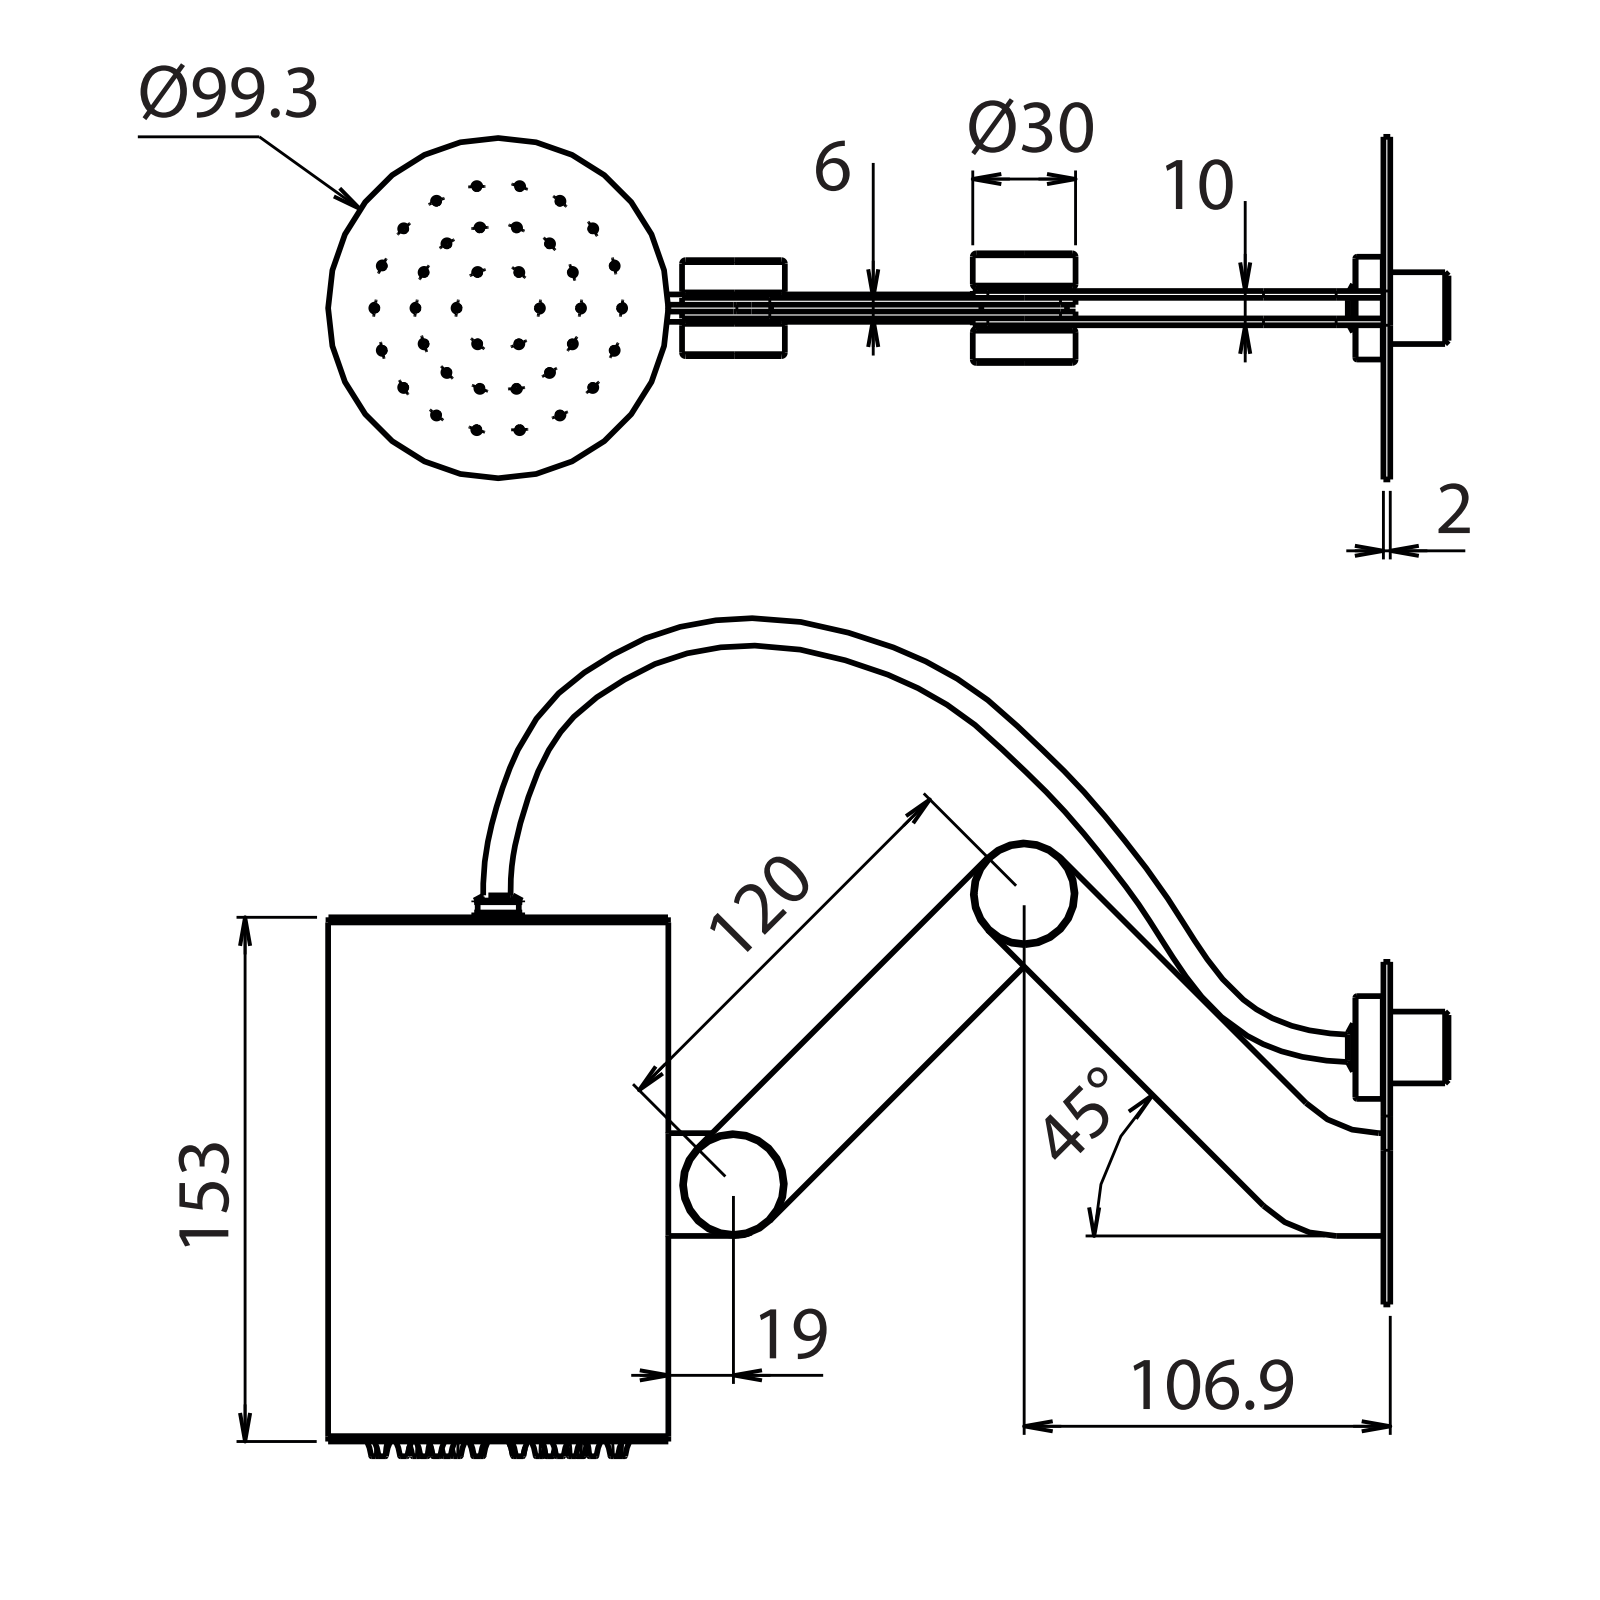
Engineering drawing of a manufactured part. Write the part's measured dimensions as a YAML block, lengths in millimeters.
part_name: "Art.62015; A.R._13811/20210511; A.R._6371/20190328; 726_20181213 (+7 more)"
step_written_by: "Spatial InterOp 3D (AUTOMOTIVE_DESIGN)"
units: millimeters
bodies: {solids: 69, faces: 1354, planar: 418, cylindrical: 385, other: 551}
overall_size: [327.01, 244.61, 100]
volume: 198773
surface_area: 264188
round_holes:
  - {diameter: 1.5, count: 38}
  - {diameter: 1.7, count: 38}
  - {diameter: 3.3, count: 38}
  - {diameter: 10.2, count: 3}
  - {diameter: 4.5, count: 2}
  - {diameter: 6, count: 2}
  - {diameter: 8.15, count: 2}
  - {diameter: 8.5, count: 2}
  - {diameter: 8.57, count: 2}
  - {diameter: 10.5, count: 2}
  - {diameter: 15.1, count: 2}
  - {diameter: 17.5, count: 2}
round_bosses_or_shafts:
  - {diameter: 10, count: 41}
  - {diameter: 5, count: 38}
  - {diameter: 30, count: 3}
  - {diameter: 16.5, count: 2}
  - {diameter: 13.9, count: 2}
  - {diameter: 13.5, count: 2}
  - {diameter: 13, count: 2}
  - {diameter: 9.6, count: 2}
partial_cylinders:
  - {radius: 0.5, count: 4}
  - {radius: 1, count: 4}
  - {radius: 2, count: 4}
  - {radius: 45, count: 4}
  - {radius: 0.1, count: 2}
  - {radius: 0.21, count: 2}
  - {radius: 0.22, count: 2}
  - {radius: 0.22, count: 2}
face_to_face_distances: [2, 4, 6, 1.5, 151.5, 8, 3, 1, 148, 150]
hole_center_spacings: [36, 46.28, 67.66, 70.91, 12.5, 10.68, 43.24, 55.16]
